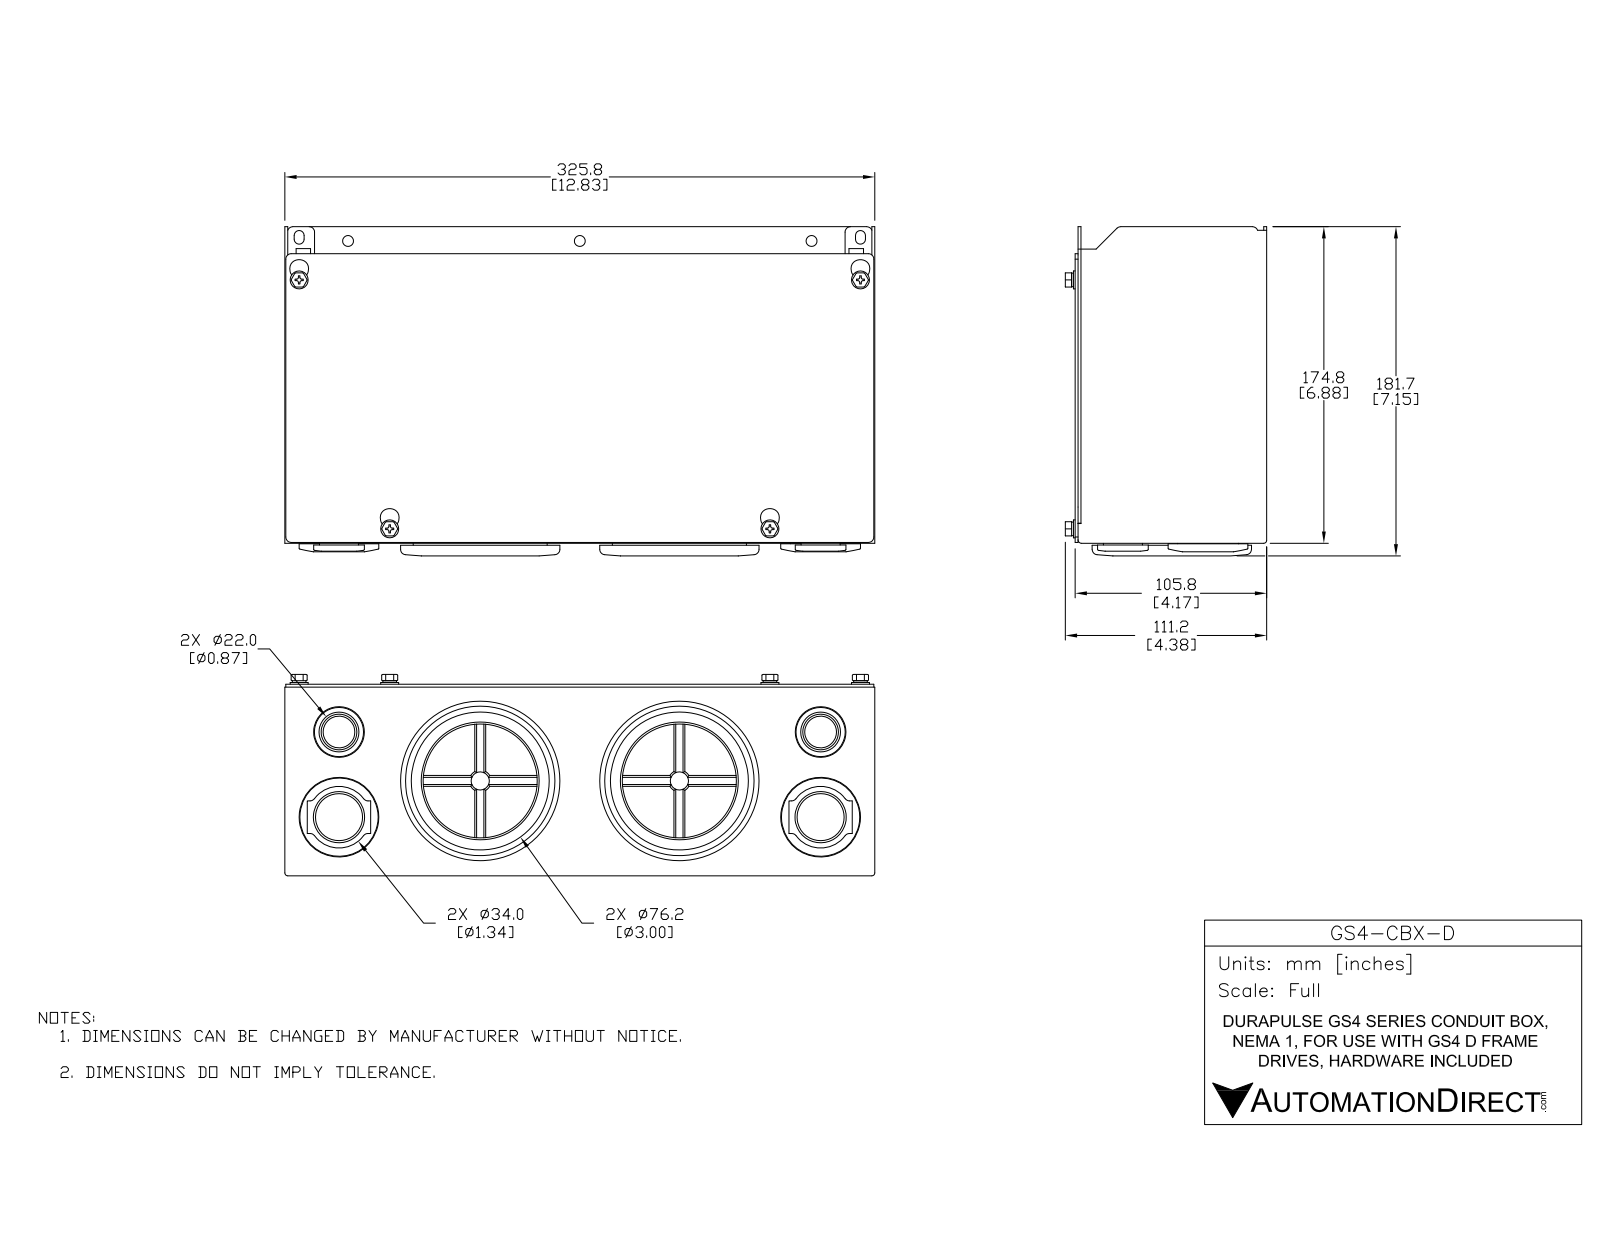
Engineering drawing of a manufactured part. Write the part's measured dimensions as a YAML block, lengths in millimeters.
part_name: "GS4-CBX-D"
step_written_by: "SolidWorks 2015 (AUTOMOTIVE_DESIGN)"
units: millimeters
bodies: {solids: 0, faces: 374, planar: 155, cylindrical: 132, other: 87}
overall_size: [325.8, 181.72, 111.2]
round_holes:
  - {diameter: 6.5, count: 4}
  - {diameter: 10.5, count: 4}
  - {diameter: 6, count: 3}
  - {diameter: 10, count: 2}
  - {diameter: 17.5, count: 2}
  - {diameter: 26, count: 2}
  - {diameter: 63, count: 2}
round_bosses_or_shafts:
  - {diameter: 9.9, count: 4}
  - {diameter: 7.5, count: 4}
  - {diameter: 88, count: 2}
  - {diameter: 44, count: 2}
  - {diameter: 28, count: 2}
  - {diameter: 8, count: 2}
partial_cylinders:
  - {radius: 1, count: 16}
  - {radius: 0.5, count: 14}
  - {radius: 3, count: 12}
  - {radius: 1.6, count: 6}
  - {radius: 2.75, count: 4}
  - {radius: 498, count: 2}
  - {radius: 2, count: 1}
  - {radius: 496.5, count: 1}
face_to_face_distances: [1.6, 104.2, 102.6, 105.8, 324.2, 322.6, 325.8, 101, 3.2, 0.5]
hole_center_spacings: [6, 146.21, 294.07, 31.13, 34.51, 47, 80.52, 82.54]
